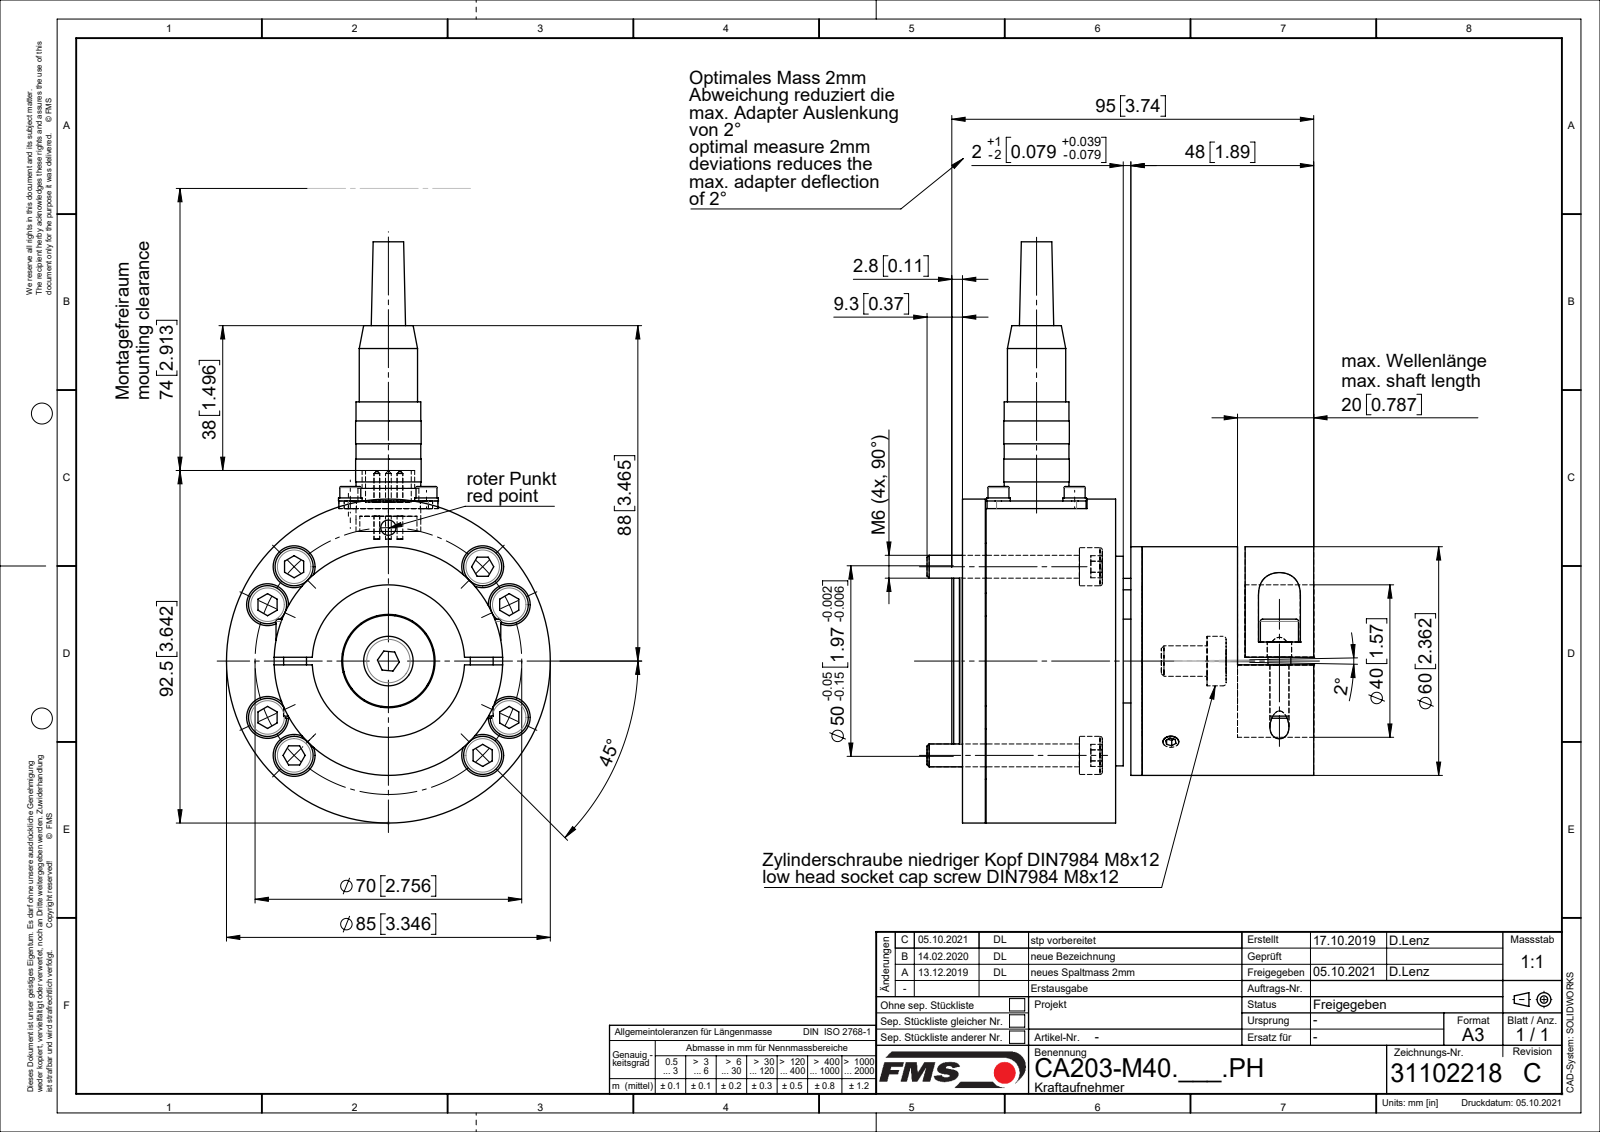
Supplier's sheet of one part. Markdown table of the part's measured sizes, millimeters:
| quantity | value |
| --- | --- |
| part name | Flanschstecker_M14x1_Mini_5pol; Zyl-Schr DIN912_M6x40; Senkniete_90°_d3x10; RKL_6203_01 (+8 more) |
| STEP written by | SolidWorks 2018 (CONFIG_CONTROL_DESIGN) |
| units | millimeters |
| bodies | 44 solids, 821 faces (294 planar, 332 cylindrical, 195 other) |
| overall size | 152.5 × 101.5 × 85 |
| volume | 288 460 mm³ |
| surface area | 109 399 mm² |
| round holes (diameter × count) | 2.5 × 8, 6.5 × 8, 11 × 8, 5 × 6, 4 × 5, 3.1 × 4, 3.2 × 4, 3.6 × 4, 7 × 4, 6.4 × 2, 3 × 1, 4.2 × 1 |
| round bosses / shafts (diameter × count) | 6 × 11, 10 × 10, 3 × 8, 1.5 × 5, 6.2 × 4, 5.7 × 4, 5.5 × 4, 85 × 1 |
| partial cylindrical surfaces (radius × count) | 2.5 × 4, 5 × 2, 5.5 × 2 |
| main face-to-face distances | 2, 30, 41, 6, 10, 45, 3, 50, 34, 20 |
| hole center spacings | 35, 20, 24.78, 25.2, 32.8, 51.14, 56.46, 28.28 |
